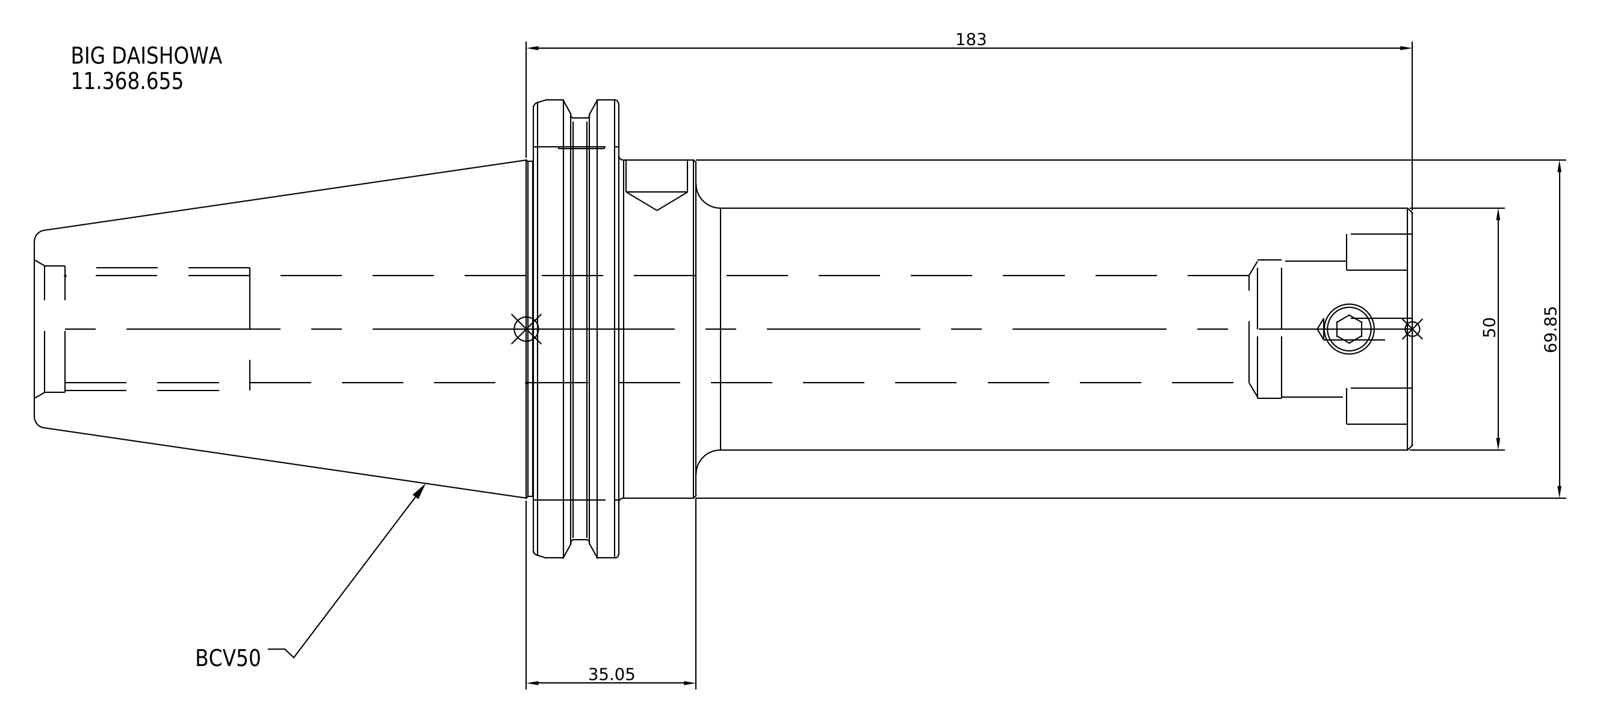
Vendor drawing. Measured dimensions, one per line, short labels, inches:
name: 11.368.655
written by: SolidWorks 2021 (CONFIG_CONTROL_DESIGN)
unit: in
bodies: 1 solid, 16 faces (7 planar, 6 cylindrical, 3 other)
size: 11.205 × 3.875 × 3.875
volume: 44.74 in³; area: 99.54 in²
bosses: 1× ⌀3.875, 1× ⌀3.594, 1× ⌀2.75, 1× ⌀1.969
face distances: 0.691, 6.455, 7.146, 5.827, 0.628, 1.319, 11.205, 5.378, 4.75, 4.059
